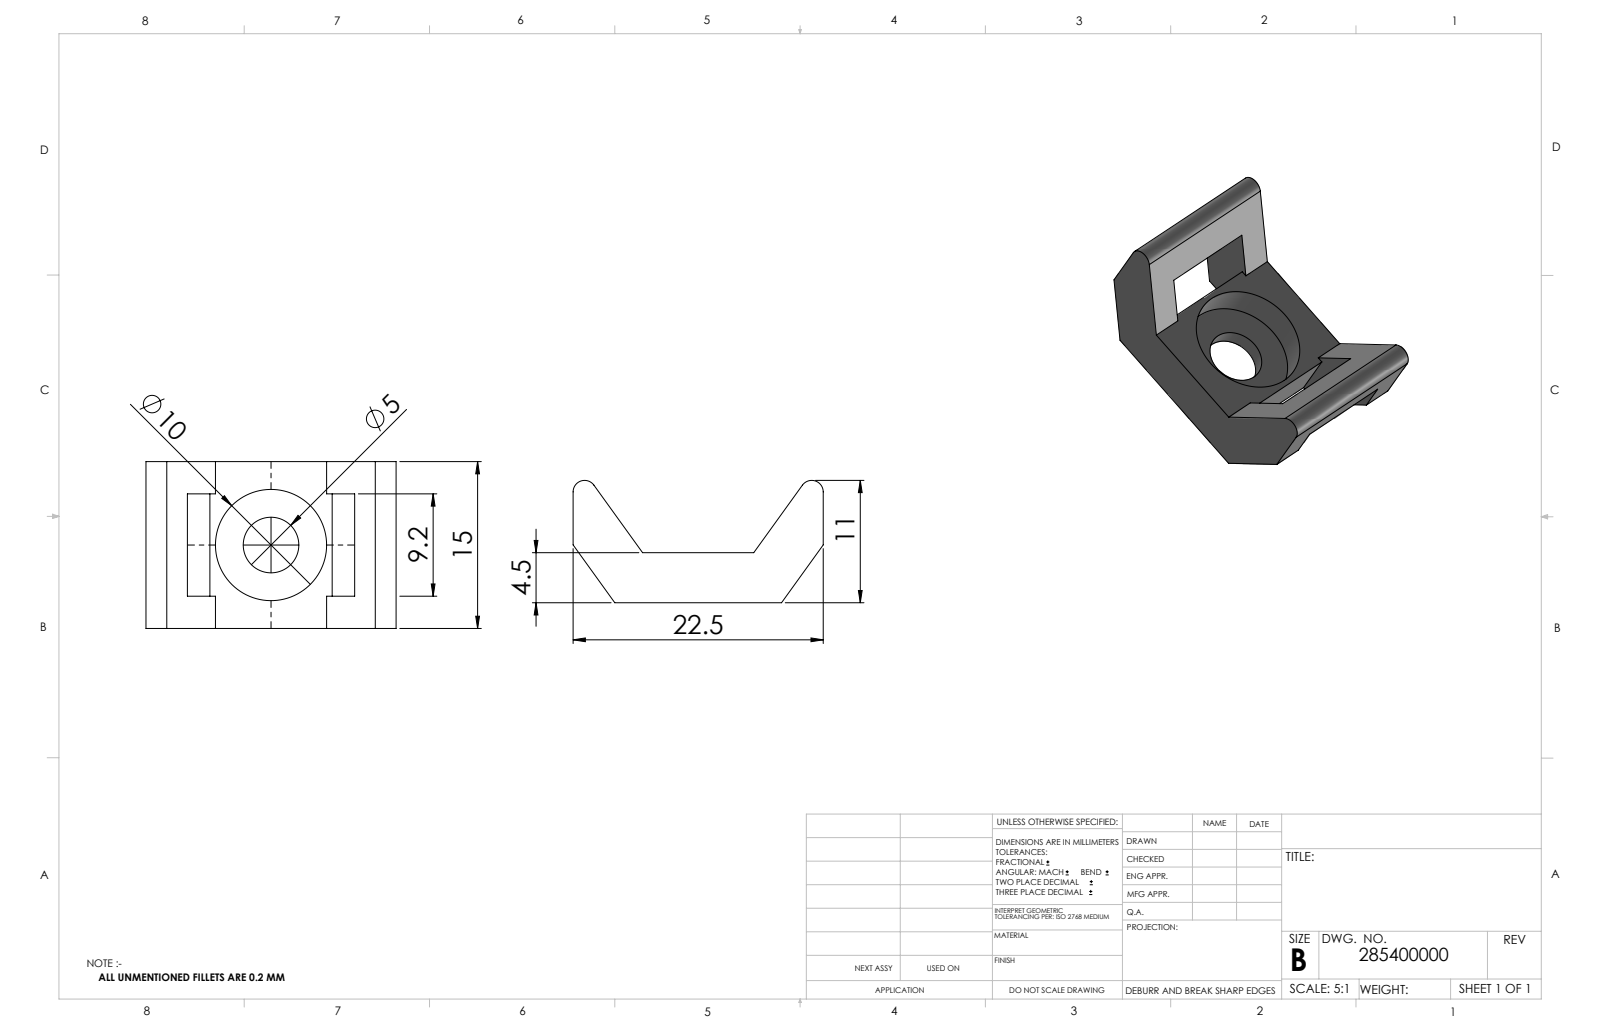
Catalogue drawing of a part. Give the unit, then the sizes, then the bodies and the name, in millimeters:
Units: millimetres
Overall size (bounding box): 22.5 × 15 × 11
Round holes (diameter × count): ⌀5 ×1, ⌀10 ×1
Partial cylindrical surfaces — rounded edges, fillets, slot ends (radius × count): R1.03 ×2
Main face-to-face distances: 2.9, 12.1, 15, 5.75, 16.75, 4.5, 4.66, 8, 3.5, 9.2
Volume: 1 097 mm³ · Surface area: 1 365 mm²
Bodies: 1 solid, 29 faces (21 planar, 8 cylindrical, 0 other)
Part name (STEP PRODUCT): 285400000_c_1
STEP written by: SolidWorks 2014 (CONFIG_CONTROL_DESIGN)
